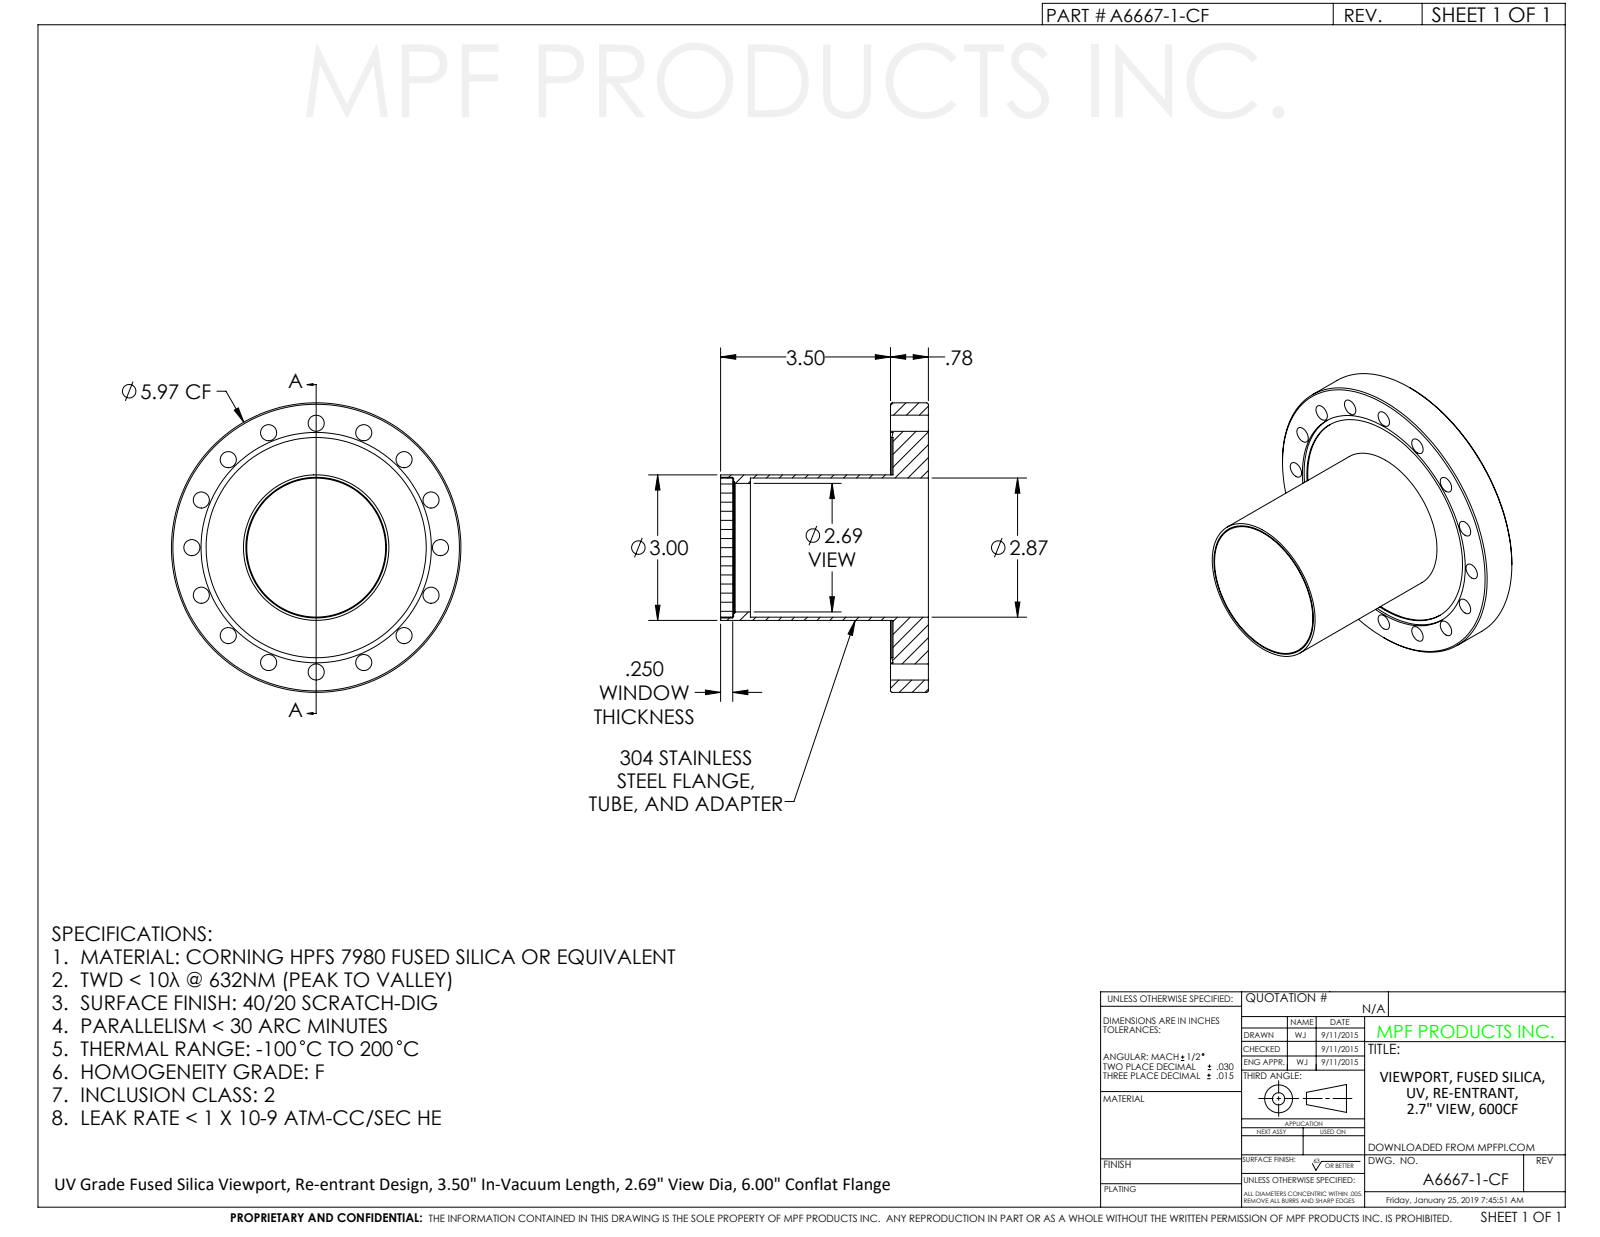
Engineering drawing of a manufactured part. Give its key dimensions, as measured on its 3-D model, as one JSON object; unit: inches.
{"part_name": "A6667-1-CF", "step_written_by": "SolidWorks 2011 (CONFIG_CONTROL_DESIGN)", "units": "inches", "bodies": {"solids": 1, "faces": 97, "planar": 17, "cylindrical": 66, "other": 14}, "overall_size": [6, 6, 4.279], "volume_in3": 19.03, "surface_area_in2": 168.3, "round_holes": [[0.332, 16], [2.69, 1], [2.735, 1], [2.865, 1], [2.87, 1], [2.96, 1], [3, 1], [4.54, 1], [4.75, 1]], "round_bosses_or_shafts": [[6, 1], [2.995, 1], [2.905, 1], [2.785, 1], [2.73, 1]], "face_to_face_distances": [0.729, 0.78, 0.051, 4.279, 3.55, 3.499, 4.029, 3.3, 3.249, 0.25], "hole_center_spacings": [1, 4.264, 4.738, 5.03, 1.963, 2.564, 3.626, 2.849]}
